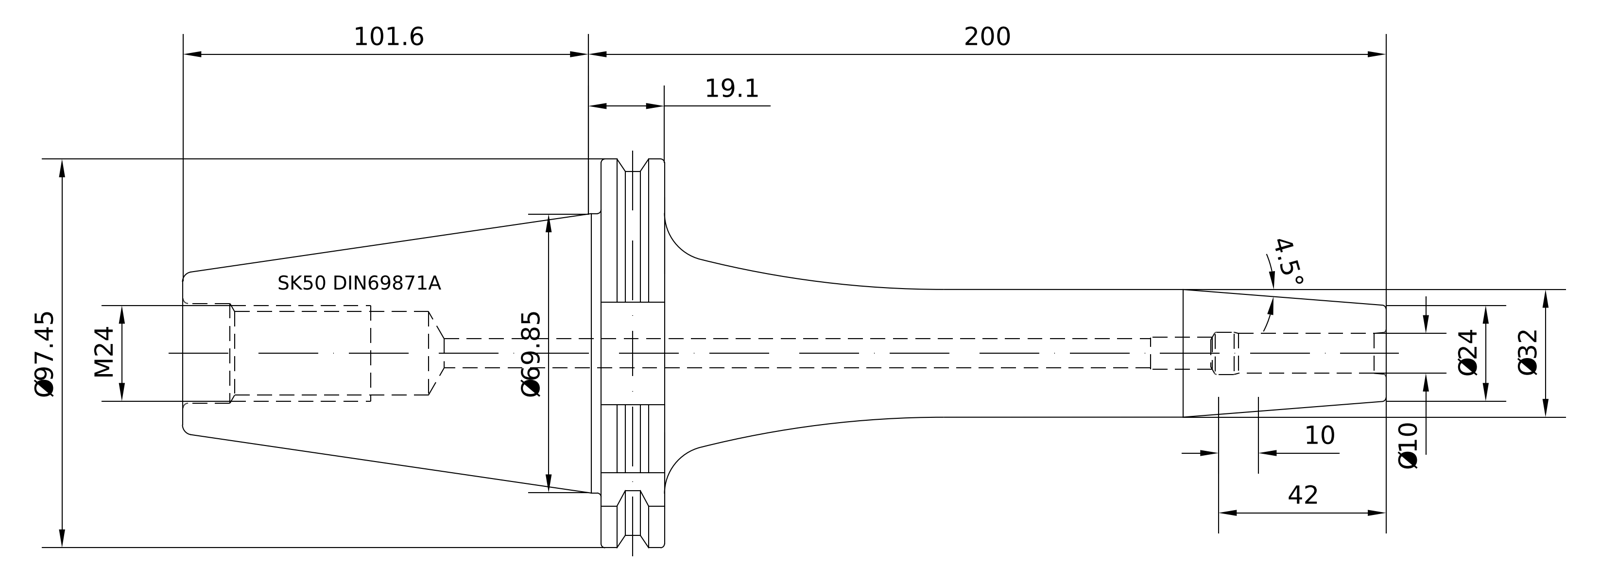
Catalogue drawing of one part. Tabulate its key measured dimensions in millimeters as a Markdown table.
| quantity | value |
| --- | --- |
| part name | 50-446-10 |
| STEP written by | PRO/ENGINEER BY PARAMETRIC TECHNOLOGY CORPORATION, 2010430 (CONFIG_CONTROL_DESIGN) |
| units | millimeters |
| bodies | 1 solid, 95 faces (21 planar, 24 cylindrical, 50 other) |
| overall size | 301.6 × 97.47 × 94 |
| volume | 502 617 mm³ |
| surface area | 61 018 mm² |
| round holes (diameter × count) | 10 × 1, 20.75 × 1, 25.01 × 1, 25.7 × 1 |
| round bosses / shafts (diameter × count) | 91 × 1, 69.15 × 1, 32 × 1, 24.01 × 1 |
| partial cylindrical surfaces (radius × count) | 1.75 × 1, 48.74 × 1 |
| main face-to-face distances | 15.85, 72.8, 104.8, 120.65, 301.6, 196.8, 180.95, 25.8, 48, 56.8 |
